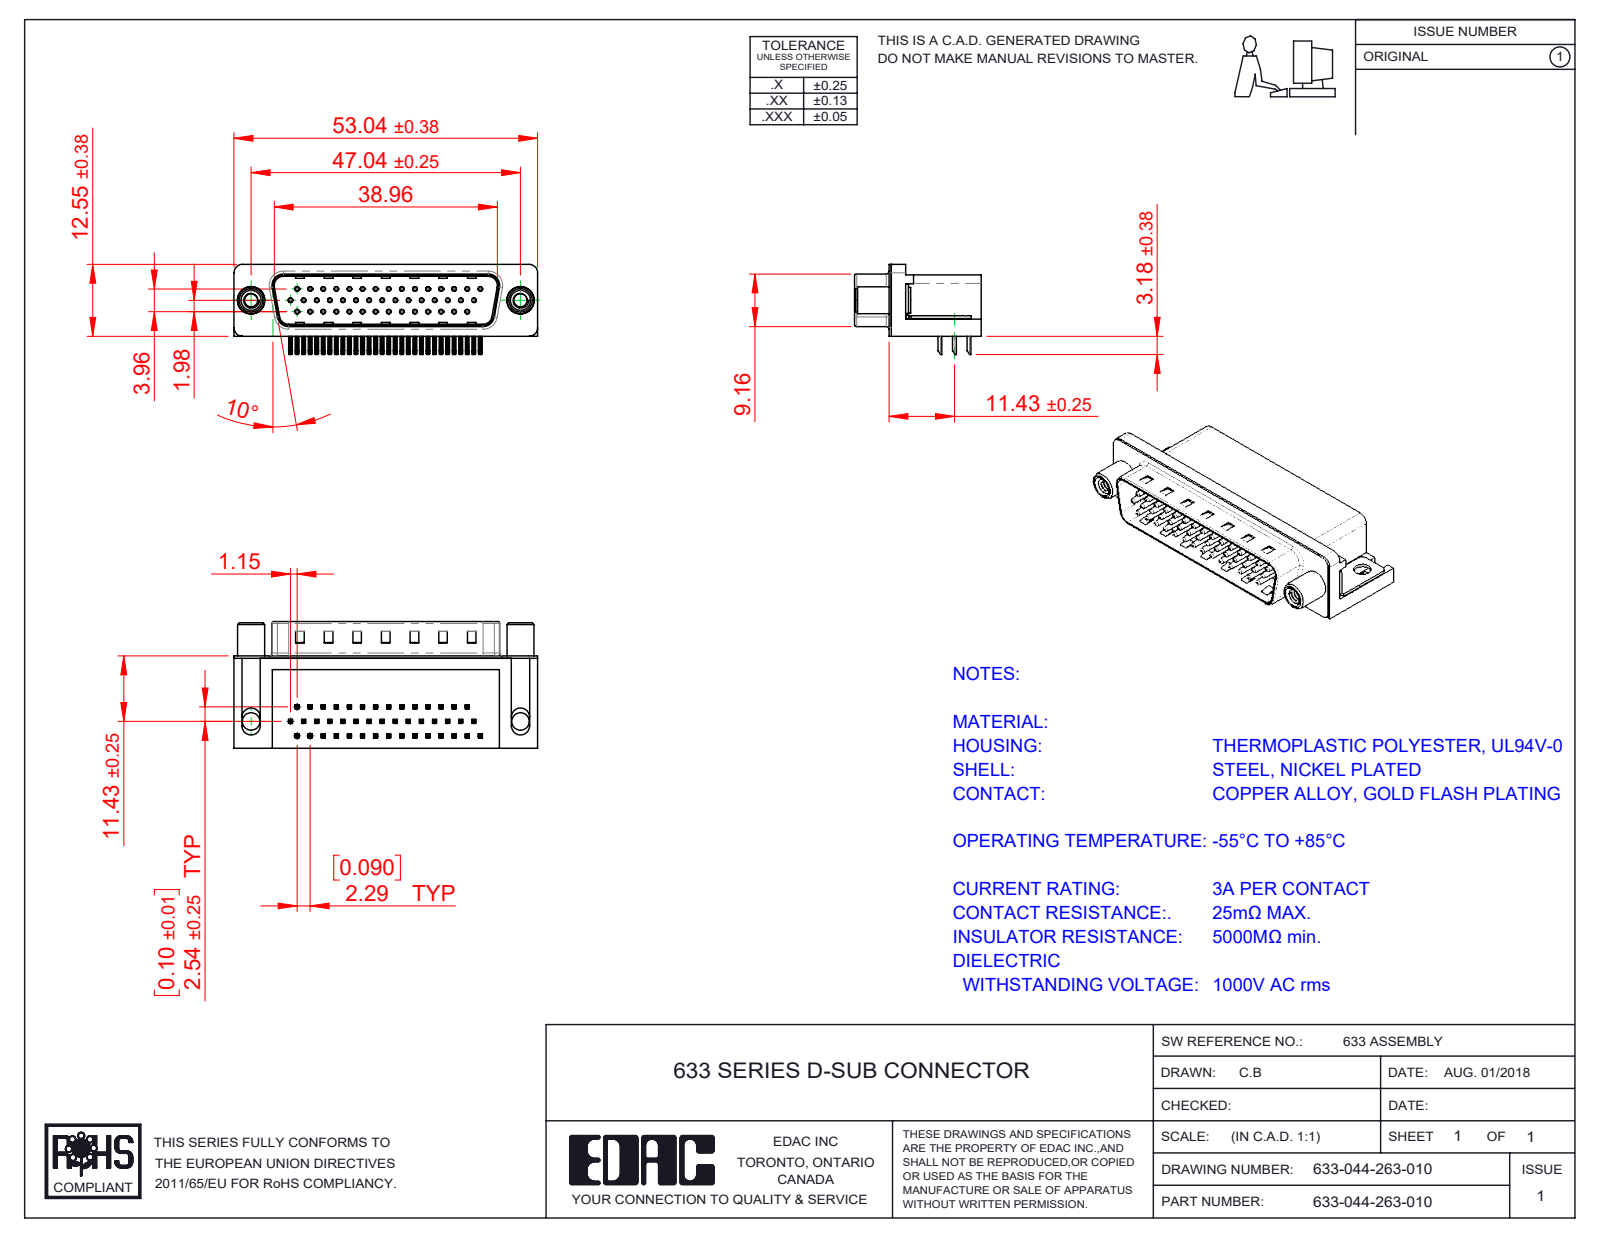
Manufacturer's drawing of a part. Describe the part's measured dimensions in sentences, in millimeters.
The part is named "633 Shell_44 Contact; 633 Housing_44 Contact; 633-044-263-010; 633 Round Threaded Standoff (+4 more)". Its 3-D file was written by "SolidWorks 2016 (CONFIG_CONTROL_DESIGN)". It is 50 solids with 3682 faces: 2307 planar, 1068 cylindrical and 307 other. Overall it measures 53.04 by 22.1 by 15.73 millimeters. Its volume is 8 203 cubic millimeters and its surface area 10 405 square millimeters. Round holes: 44 of diameter 0.35, 44 of diameter 0.8, 2 of diameter 2.3, 2 of diameter 3.05, 2 of diameter 3.1, 2 of diameter 4, 2 of diameter 4.8, 2 of diameter 5. Round bosses or shafts: 44 of diameter 0.75, 2 of diameter 4.9, 2 of diameter 4.7, 2 of diameter 4.5, 2 of diameter 3.85. Partial cylindrical surfaces (rounded edges, fillets, slot ends): 176 of radius 0.25, 88 of radius 0.12, 16 of radius 1, 9 of radius 0.5, 8 of radius 1.6, 7 of radius 1.5, 4 of radius 0.9, 4 of radius 2. The main face-to-face distances are 0.4, 10.35, 15.7, 2.9, 8.76, 2.5, 2.1, 2.54, 16.1, 10.7. The hole center spacings are 2.29, 4.57, 4.58, 2.28, 6.87, 9.16, 11.45, 2.27.
